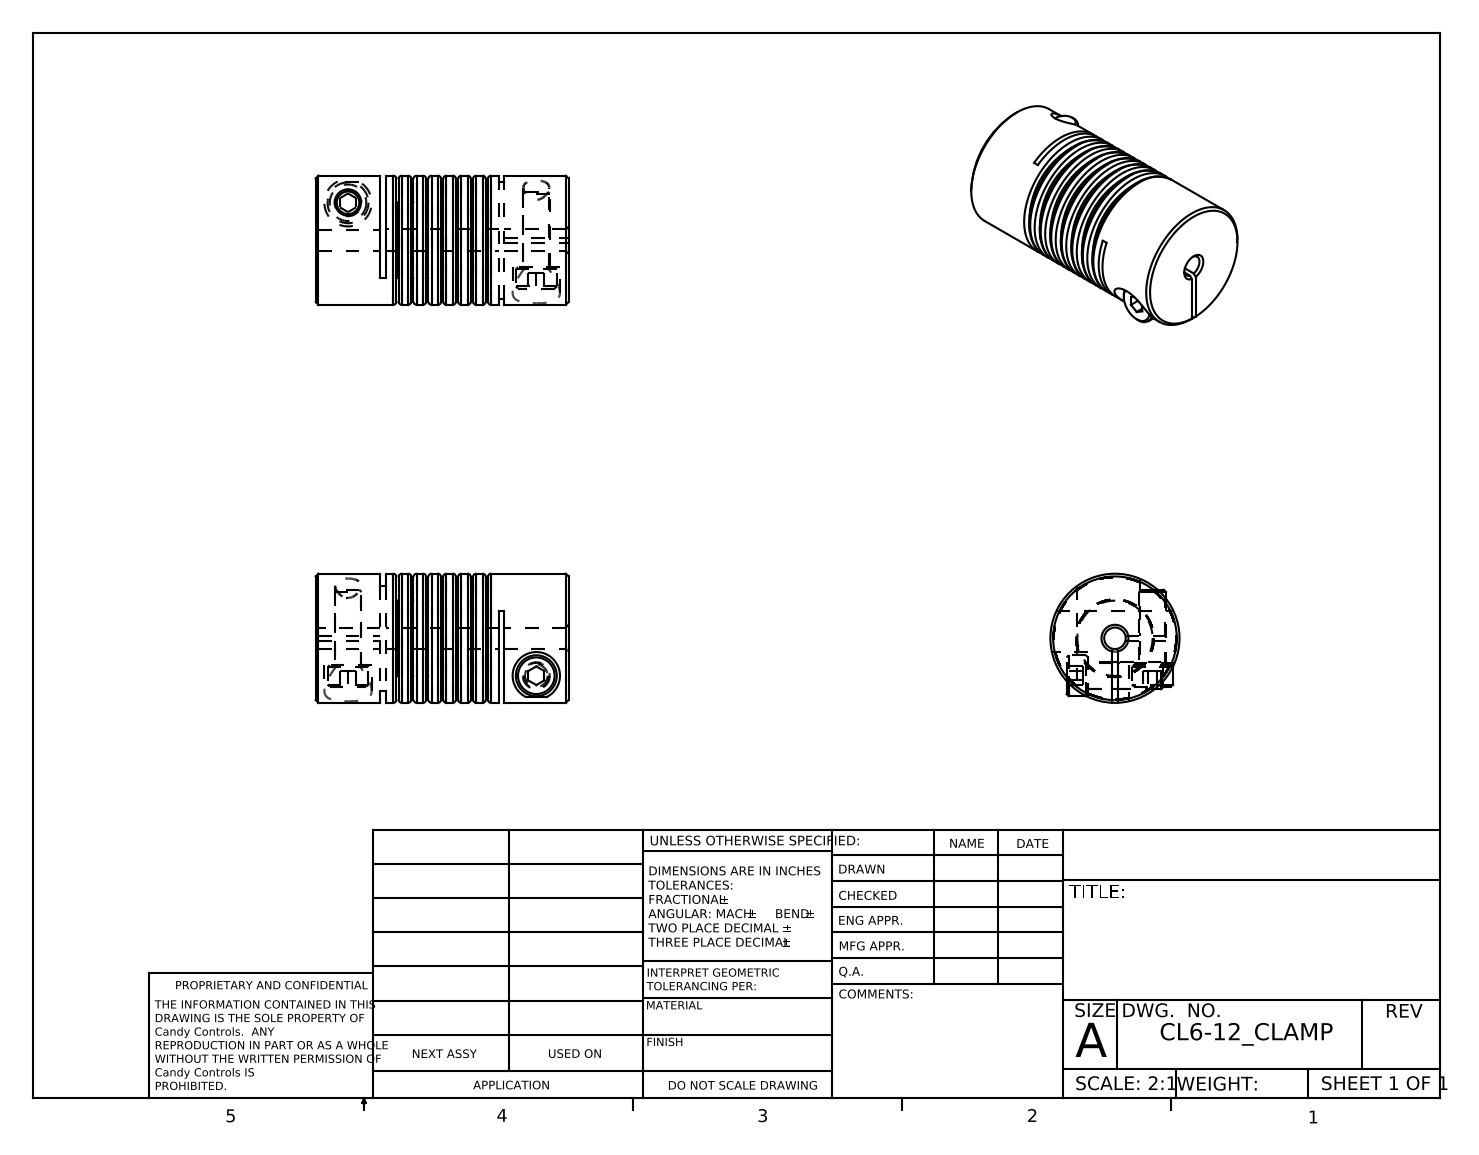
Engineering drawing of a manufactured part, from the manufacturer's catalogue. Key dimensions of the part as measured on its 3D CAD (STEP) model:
Part name (STEP PRODUCT): CL6-12_CLAMP
STEP written by: SolidWorks 2010 (CONFIG_CONTROL_DESIGN)
Units: millimetres
Bodies: 3 solids, 169 faces (48 planar, 44 cylindrical, 77 other)
Overall size (bounding box): 23.5 × 12 × 12
Volume: 2 328 mm³ · Surface area: 2 930 mm²
Round holes (diameter × count): ⌀2.4 ×2, ⌀4.4 ×2, ⌀2 ×1
Round bosses / shafts (diameter × count): ⌀3.8 ×2, ⌀2.5 ×2, ⌀12 ×1
Main face-to-face distances: 1.38, 2.77, 4.15, 5.53, 6.92, 1.39, 1.58, 2.97, 4.35, 1.18
